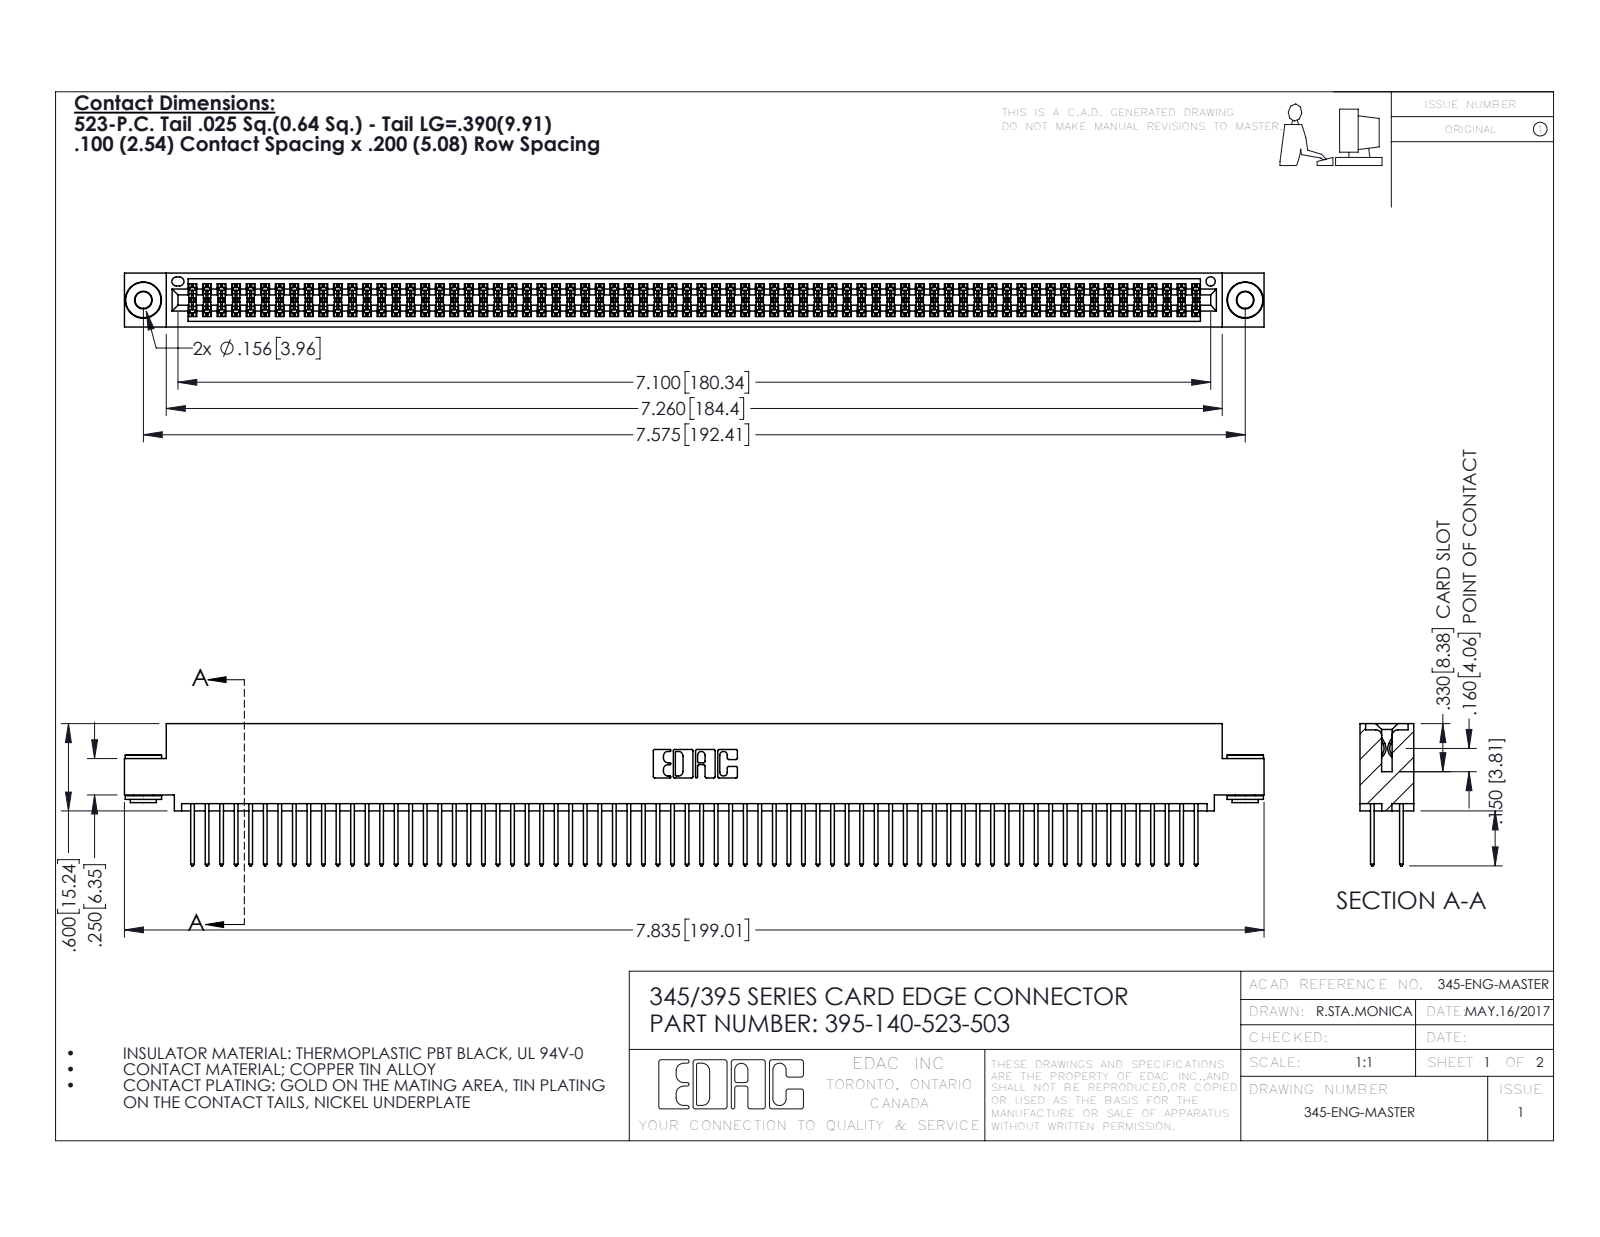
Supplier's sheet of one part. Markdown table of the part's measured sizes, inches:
| quantity | value |
| --- | --- |
| part name | 345-250-002_345-250-002-102; 395-140-523-503; 345-292-001_345-293-123; 345 Part_0.110 Offset - 0.156 Dia-TH |
| STEP written by | SolidWorks 2016 (CONFIG_CONTROL_DESIGN) |
| units | inches |
| bodies | 143 solids, 7168 faces (4714 planar, 2446 cylindrical, 8 other) |
| overall size | 7.835 × 0.977 × 0.37 |
| volume | 1.21 in³ |
| surface area | 48.72 in² |
| round holes (diameter × count) | 0.116 × 2, 0.156 × 2, 0.064 × 1 |
| round bosses / shafts (diameter × count) | 0.25 × 2, 0.18 × 2, 0.136 × 2 |
| partial cylindrical surfaces (radius × count) | 0.006 × 210, 0.01 × 140, 0.01 × 22, 0.007 × 6, 0.031 × 6, 0.026 × 3, 0.014 × 2, 0.019 × 2 |
| main face-to-face distances | 0.072, 0.298, 0.2, 0.025, 0.098, 0.272, 0.37, 0.225, 0.175, 0.149 |
| hole center spacings | 0.27, 7.339, 7.575 |
